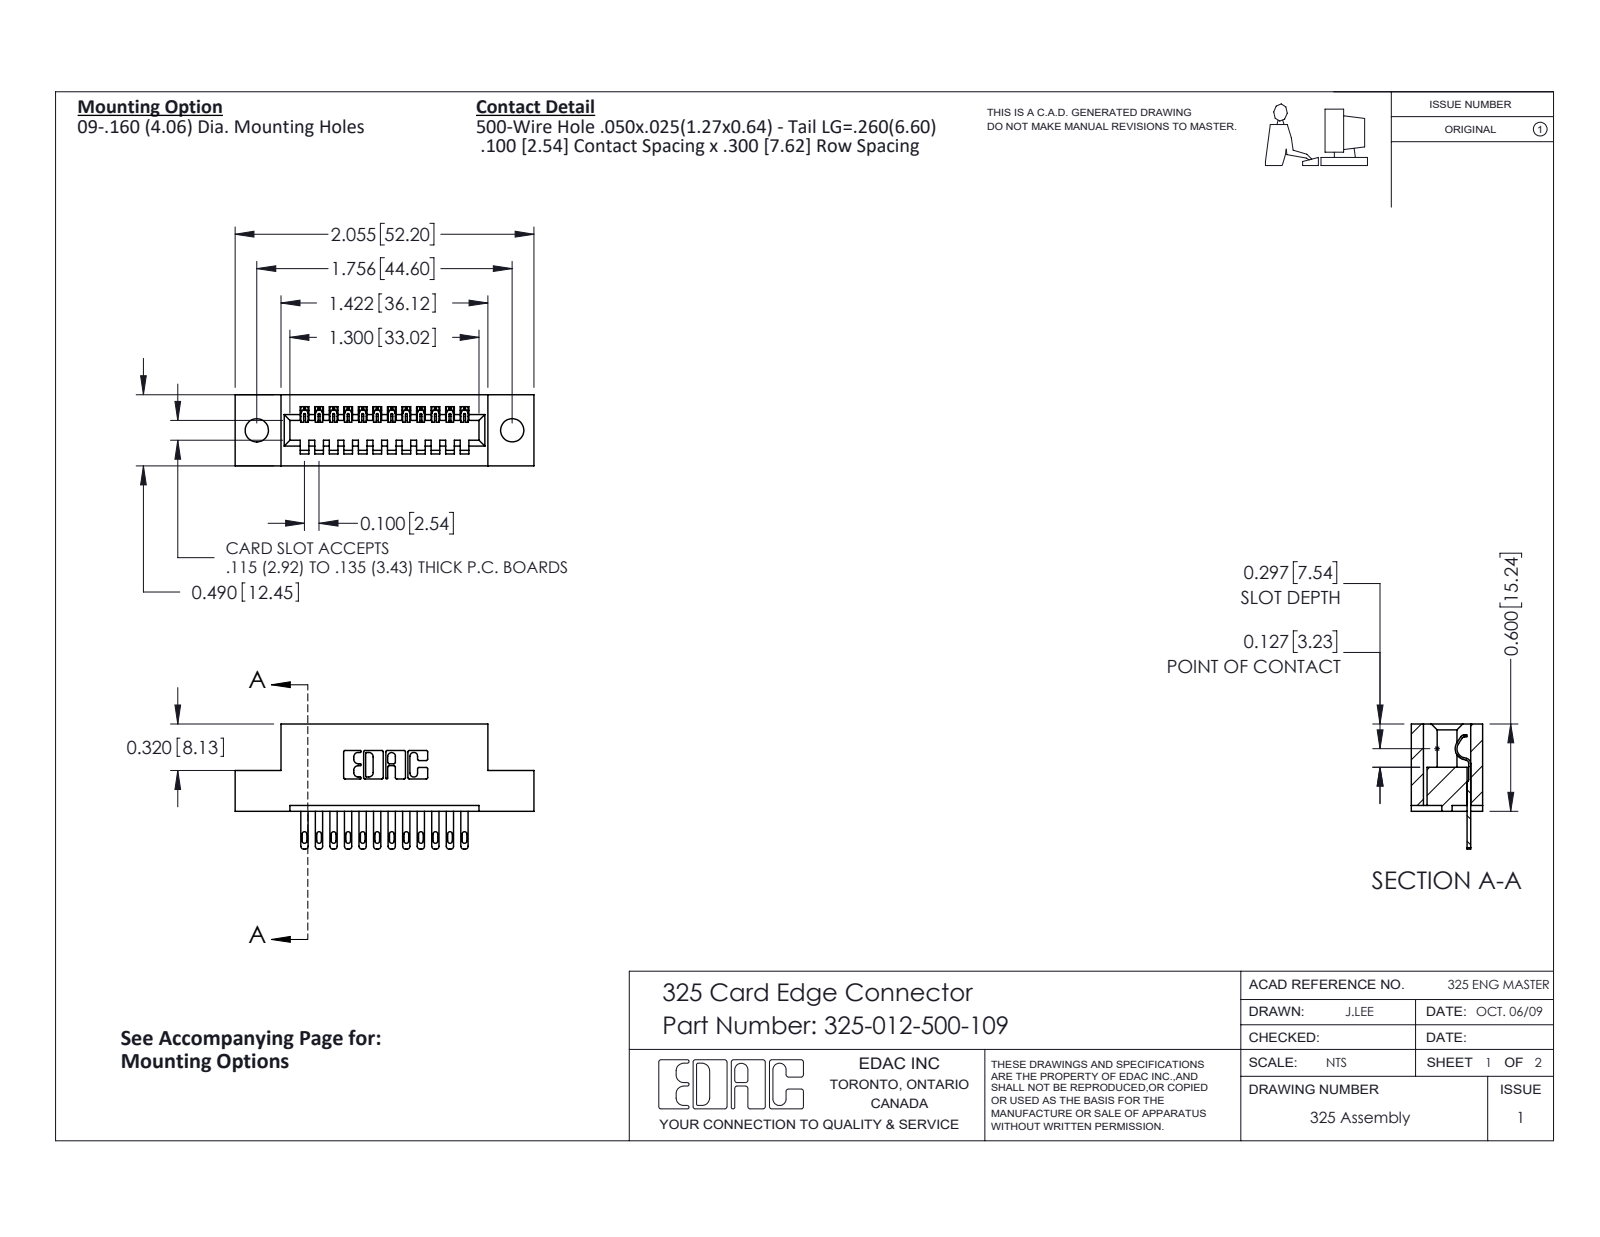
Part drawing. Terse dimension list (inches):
name: 325-012-500-109; 325-292-001_325-293-100; 325 Part_.160 TH
written by: SolidWorks 2016 (CONFIG_CONTROL_DESIGN)
unit: in
bodies: 13 solids, 762 faces (502 planar, 260 cylindrical, 0 other)
size: 2.055 × 0.86 × 0.49
volume: 0.376 in³; area: 9.536 in²
holes: 2× ⌀0.16
rounds: 24× R0.006, 24× R0.016, 24× R0.02, 22× R0.01, 6× R0.007, 6× R0.031, 3× R0.026, 1× R0.014
face distances: 0.3, 0.083, 0.407, 0.49, 0.04, 0.1, 0.2, 0.6, 0.107, 0.383
hole spacings: 1.756
